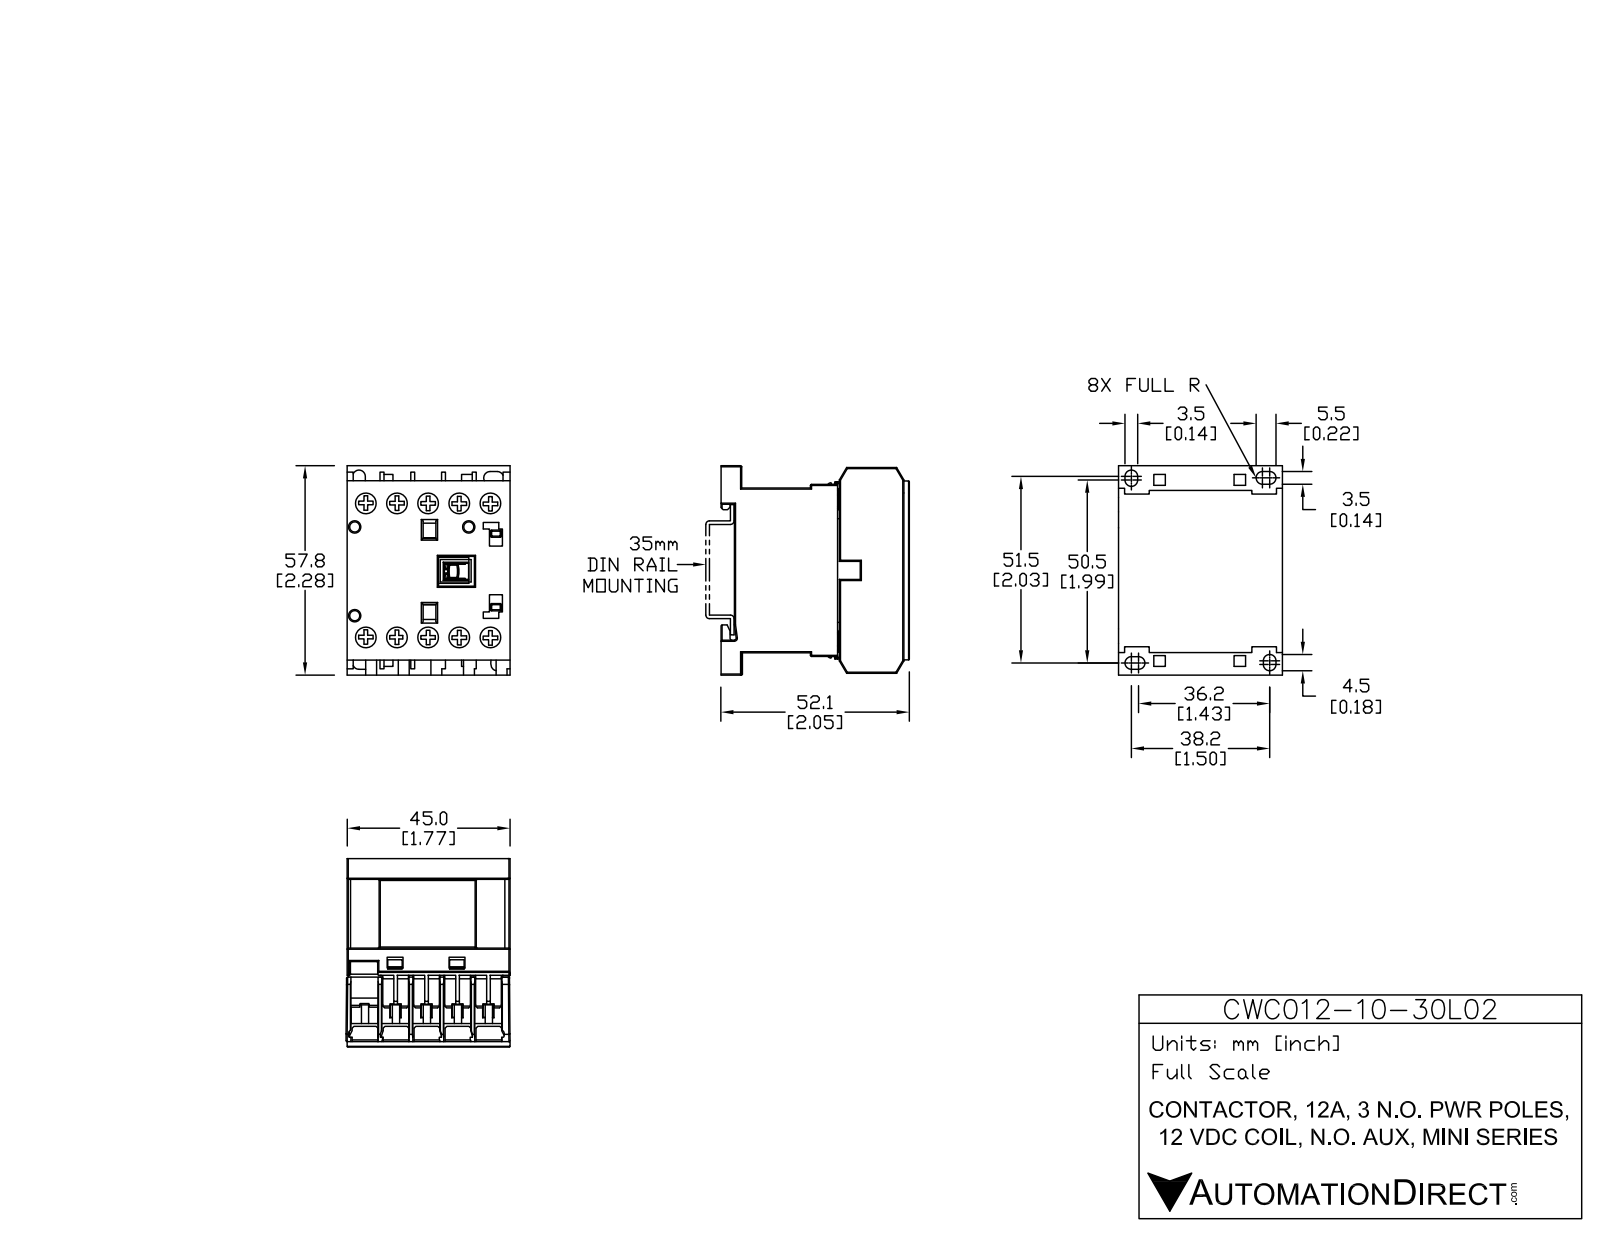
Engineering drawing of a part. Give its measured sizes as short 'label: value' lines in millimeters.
name: CWC12-10-30L02
written by: SolidWorks 2013 (AUTOMOTIVE_DESIGN)
unit: mm
bodies: 15 solids, 535 faces (445 planar, 90 cylindrical, 0 other)
size: 58.04 × 52.12 × 45.75
volume: 97 133 mm³; area: 30 437 mm²
holes: 10× ⌀6.2, 3× ⌀2.8
bosses: 10× ⌀5.9
rounds: 20× R0.3, 6× R1.72, 2× R1.73, 1× R0.32, 1× R0.42, 1× R0.55
face distances: 8.25, 45.5, 1.25, 16.5, 9.5, 5.5, 17.75, 5.13, 10.63, 7
hole spacings: 8.55, 37.94, 17.1, 40.72, 36.96, 25.65, 44.99, 6.91
